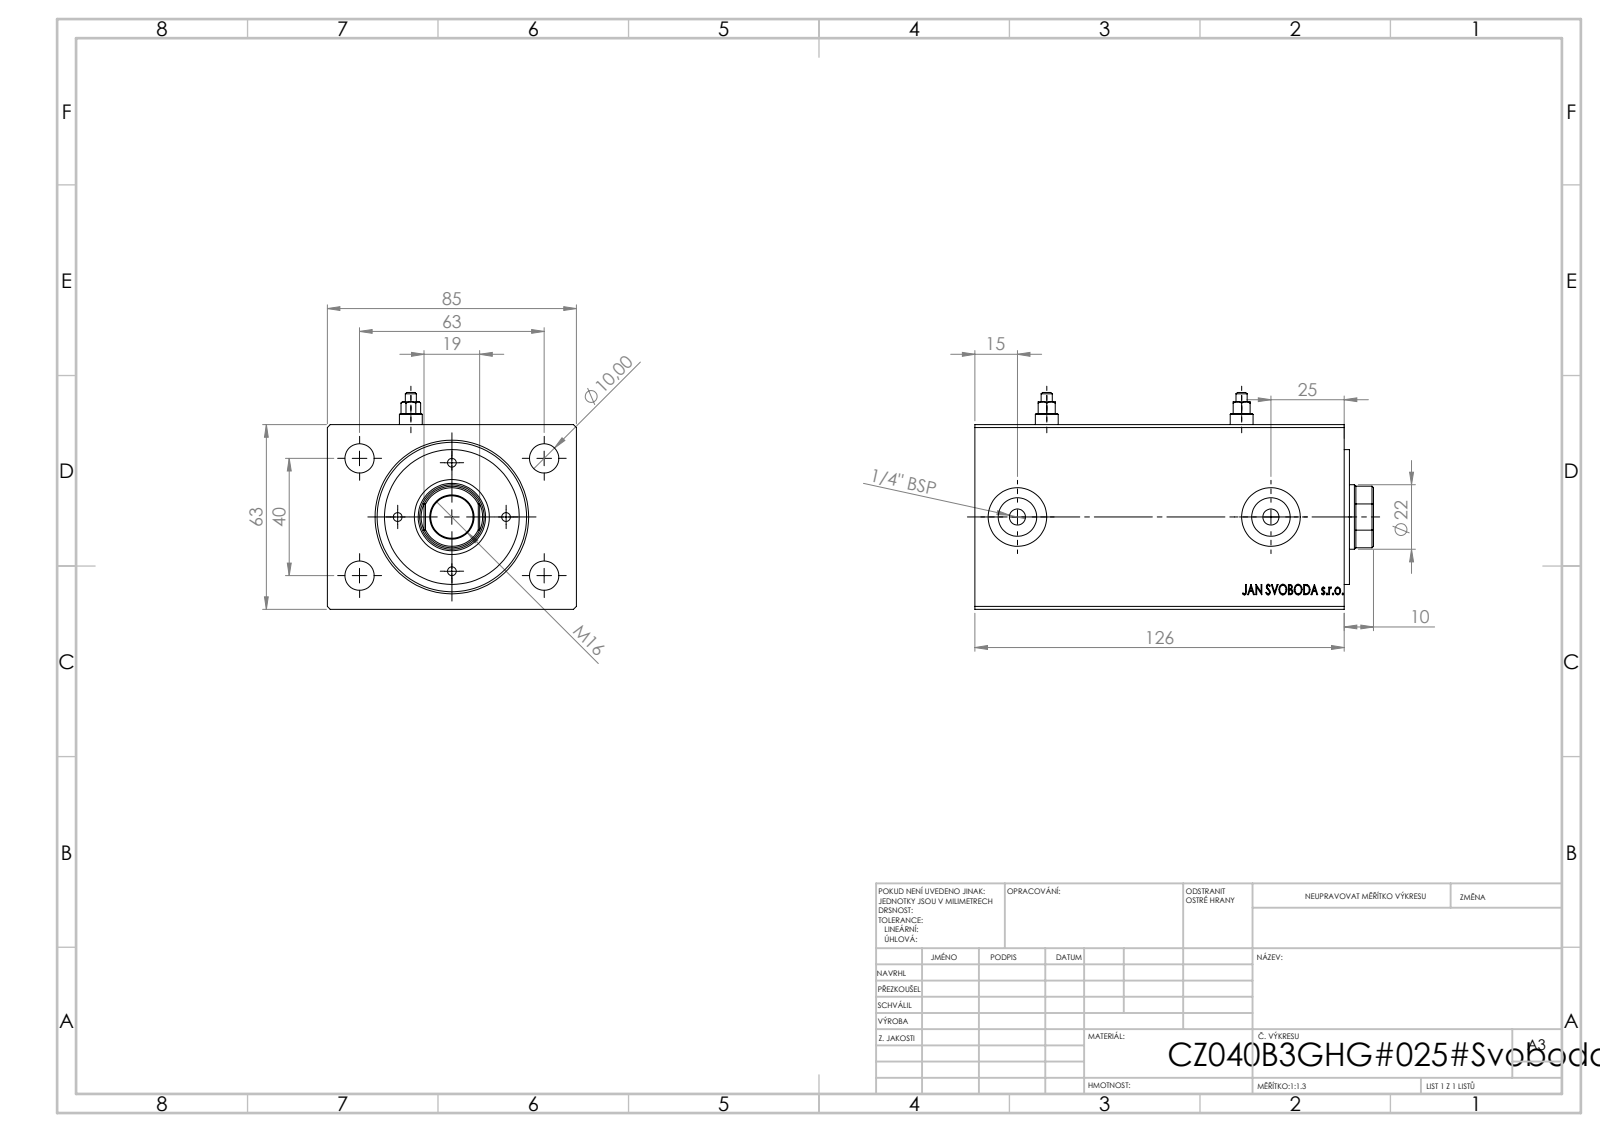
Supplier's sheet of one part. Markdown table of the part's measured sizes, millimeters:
| quantity | value |
| --- | --- |
| part name | Zatka_Cushioning3; V500CZ_B_VC; V500CZ |
| STEP written by | SolidWorks 2019 (CONFIG_CONTROL_DESIGN) |
| units | millimeters |
| bodies | 5 solids, 934 faces (424 planar, 74 cylindrical, 436 other) |
| overall size | 136 × 85 × 74 |
| volume | 631 265 mm³ |
| surface area | 92 112 mm² |
| round holes (diameter × count) | 3 × 4, 10 × 4, 1.8 × 2, 5.5 × 2, 8 × 2, 13.16 × 2, 20 × 2, 14.5 × 1, 22 × 1, 23 × 1, 36 × 1, 40 × 1 |
| round bosses / shafts (diameter × count) | 7.8 × 2, 3.8 × 2, 46 × 1 |
| partial cylindrical surfaces (radius × count) | 10.5 × 1 |
| main face-to-face distances | 63, 85, 126, 110.7, 15.3, 10, 1.8, 8.2, 102.5, 117.8 |
| hole center spacings | 18.5, 23.85, 26.16, 31.54, 37.31, 49.74, 53.85, 37 |
